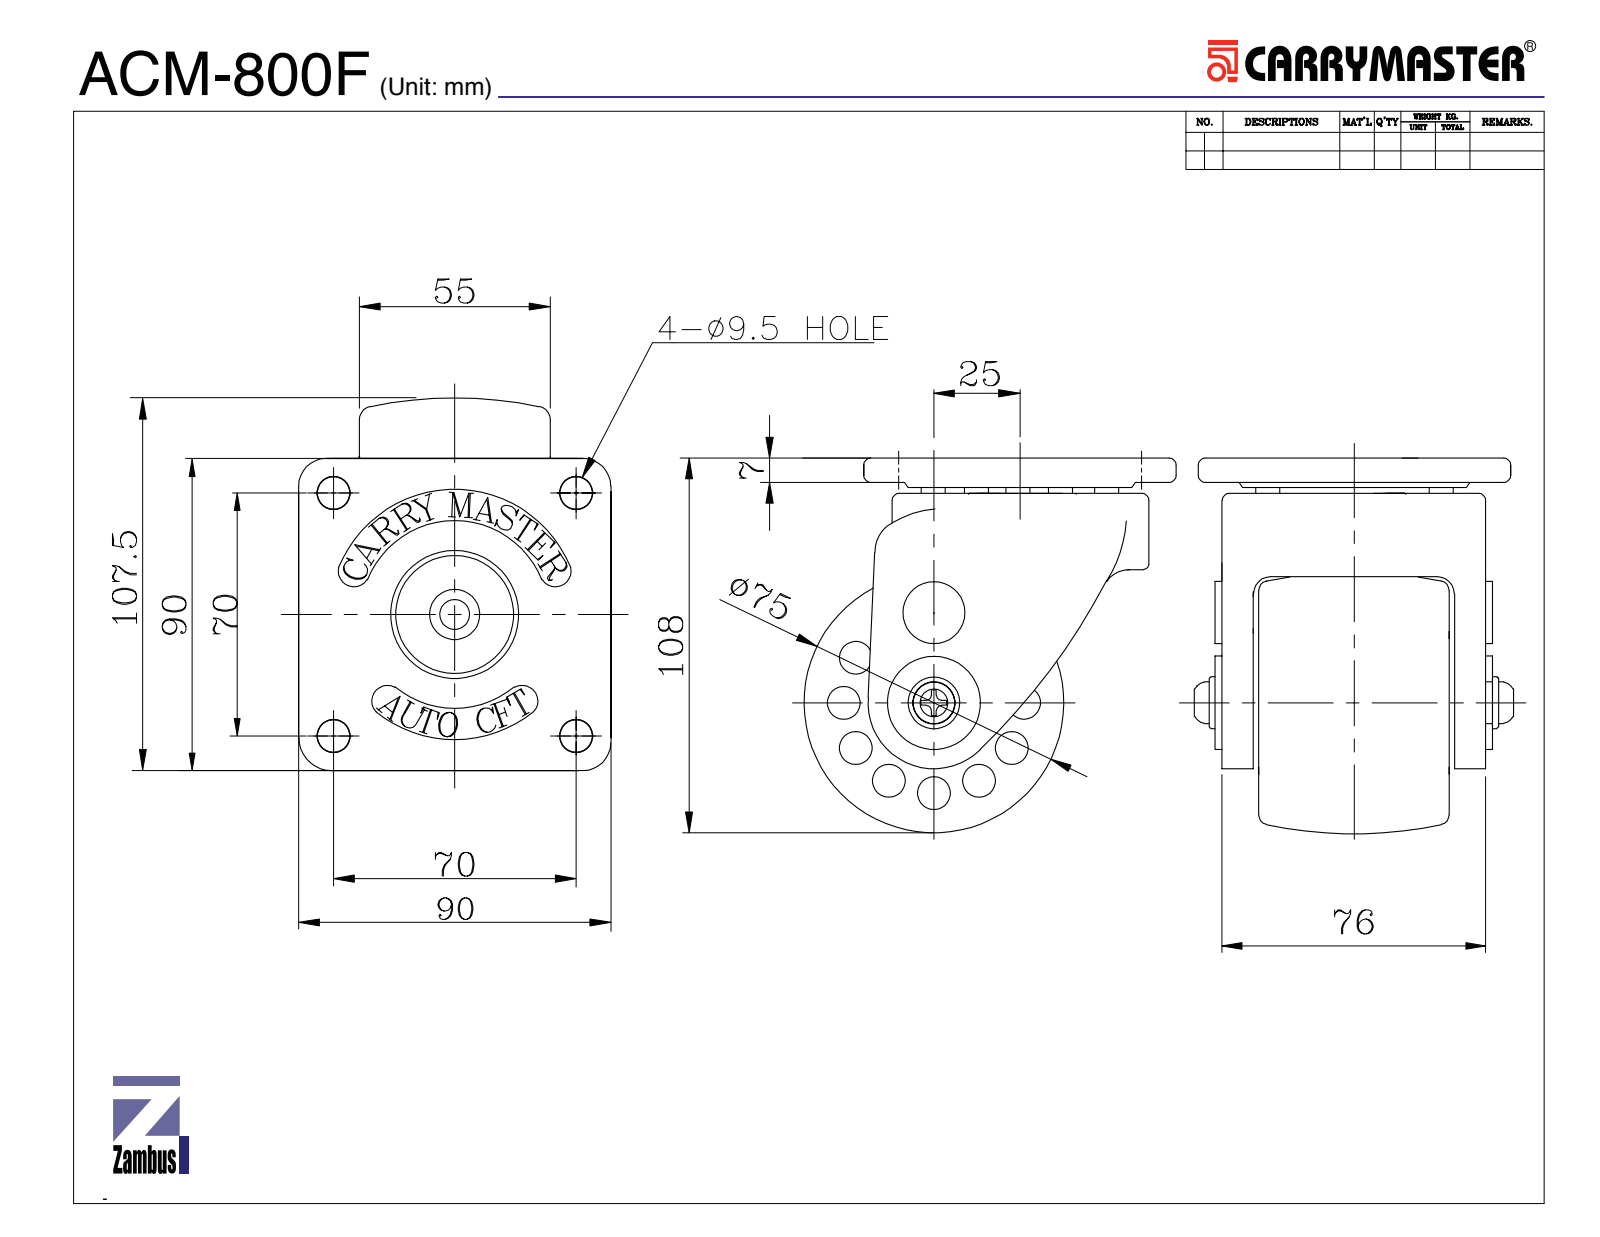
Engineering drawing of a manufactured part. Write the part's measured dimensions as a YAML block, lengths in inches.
part_name: "ACM-800F"
step_written_by: "SolidWorks 2015 (CONFIG_CONTROL_DESIGN)"
units: inches
bodies: {solids: 34, faces: 1169, planar: 569, cylindrical: 118, other: 482}
overall_size: [4.232, 4.232, 3.543]
volume: 25.84
surface_area: 142.1
round_holes:
  - {diameter: 0.374, count: 4}
  - {diameter: 0.056, count: 1}
  - {diameter: 0.268, count: 1}
  - {diameter: 0.394, count: 1}
  - {diameter: 0.512, count: 1}
  - {diameter: 0.709, count: 1}
  - {diameter: 0.787, count: 1}
  - {diameter: 1.575, count: 1}
round_bosses_or_shafts:
  - {diameter: 1.622, count: 1}
  - {diameter: 1.496, count: 1}
  - {diameter: 0.984, count: 1}
  - {diameter: 0.945, count: 1}
  - {diameter: 0.827, count: 1}
  - {diameter: 0.709, count: 1}
  - {diameter: 0.65, count: 1}
  - {diameter: 0.551, count: 1}
partial_cylinders:
  - {radius: 0.079, count: 8}
  - {radius: 0.157, count: 4}
  - {radius: 0.374, count: 4}
  - {radius: 0.049, count: 2}
  - {radius: 0.058, count: 2}
  - {radius: 0.394, count: 2}
  - {radius: 0.512, count: 2}
  - {radius: 0.043, count: 1}
face_to_face_distances: [0.276, 0.413, 2.579, 2.165, 0.039, 0.059, 0.379, 0.197, 0.104, 0.079]
hole_center_spacings: [1.949, 2.756, 3.897, 0.543, 0.824, 1.024]
